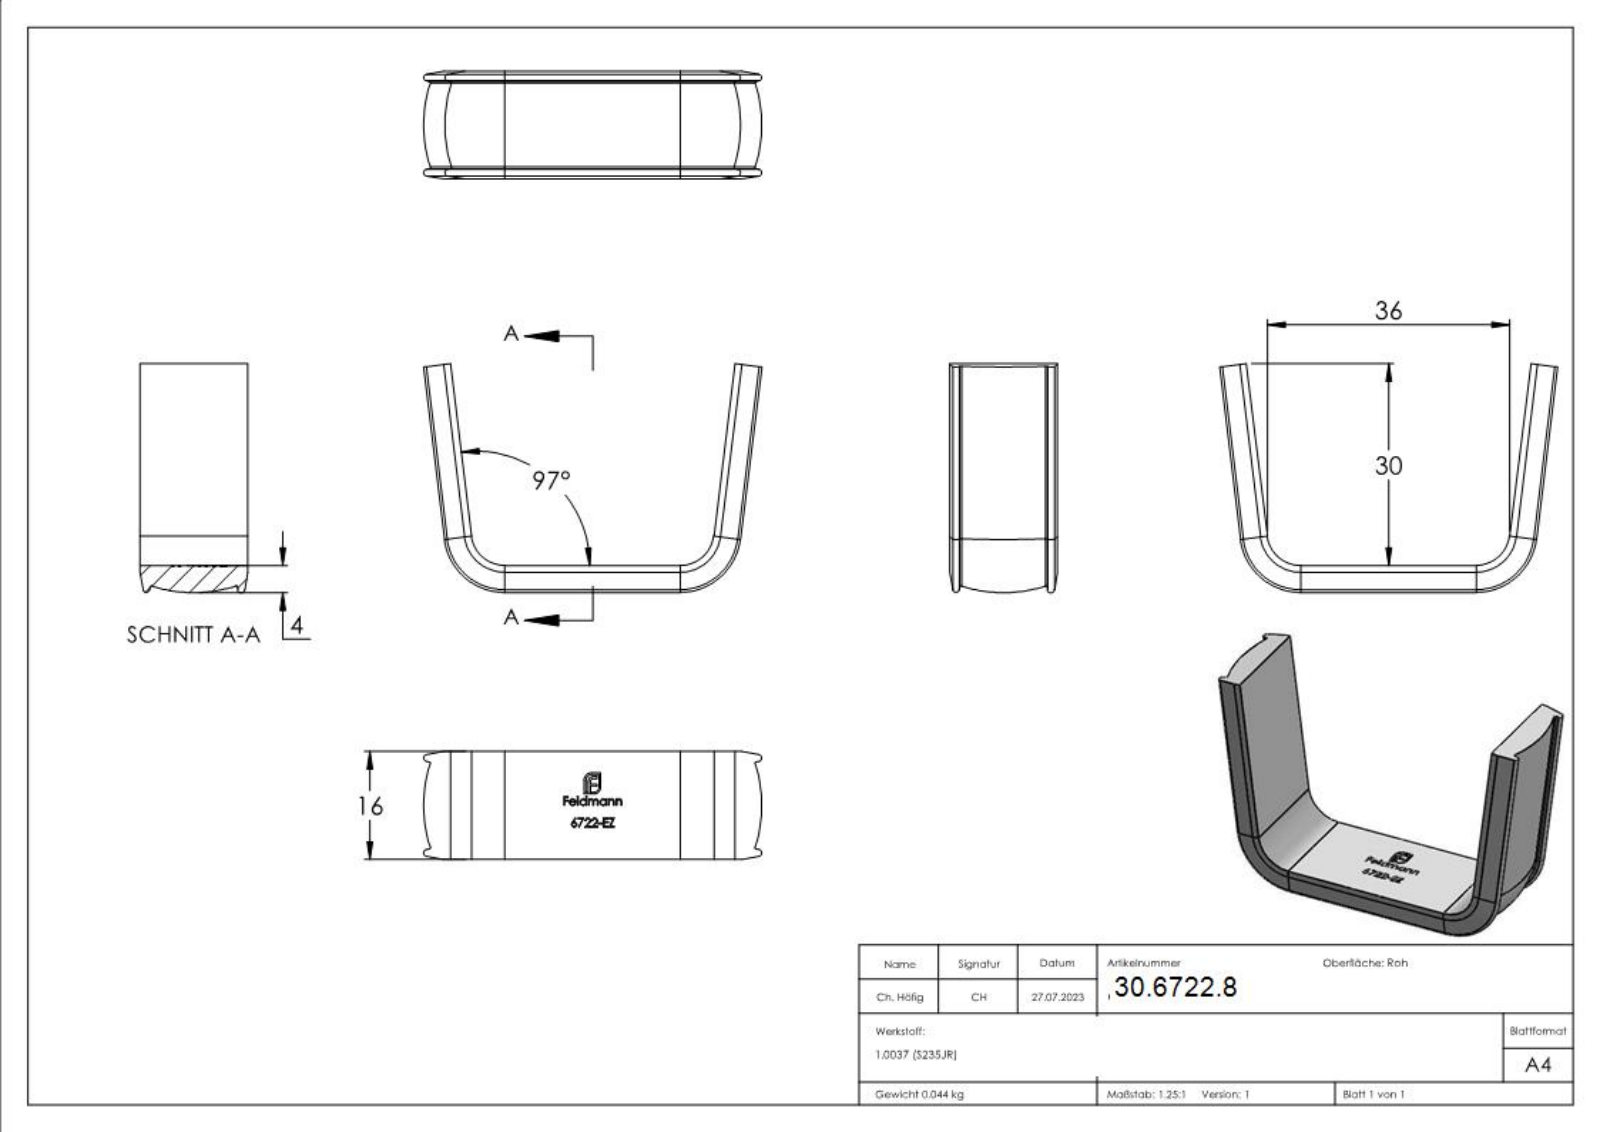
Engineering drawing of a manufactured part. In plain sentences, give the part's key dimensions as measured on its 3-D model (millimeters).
The part is named "6722-EZ". Its 3-D file was written by "SolidWorks 2018 (CONFIG_CONTROL_DESIGN)". It is 1 solid with 292 faces: 168 planar, 17 cylindrical and 107 other. Overall it measures 50.23 by 34 by 16 millimeters. Its volume is 5 611 cubic millimeters and its surface area 4 053 square millimeters. Partial cylindrical surfaces (rounded edges, fillets, slot ends): 6 of radius 0.2, 6 of radius 0.5, 3 of radius 20.07, 2 of radius 5. The main face-to-face distances are 16, 13.89, 13.9, 2.2, 3.15, 1.32, 0.63, 11.2, 4.8, 3.2.
